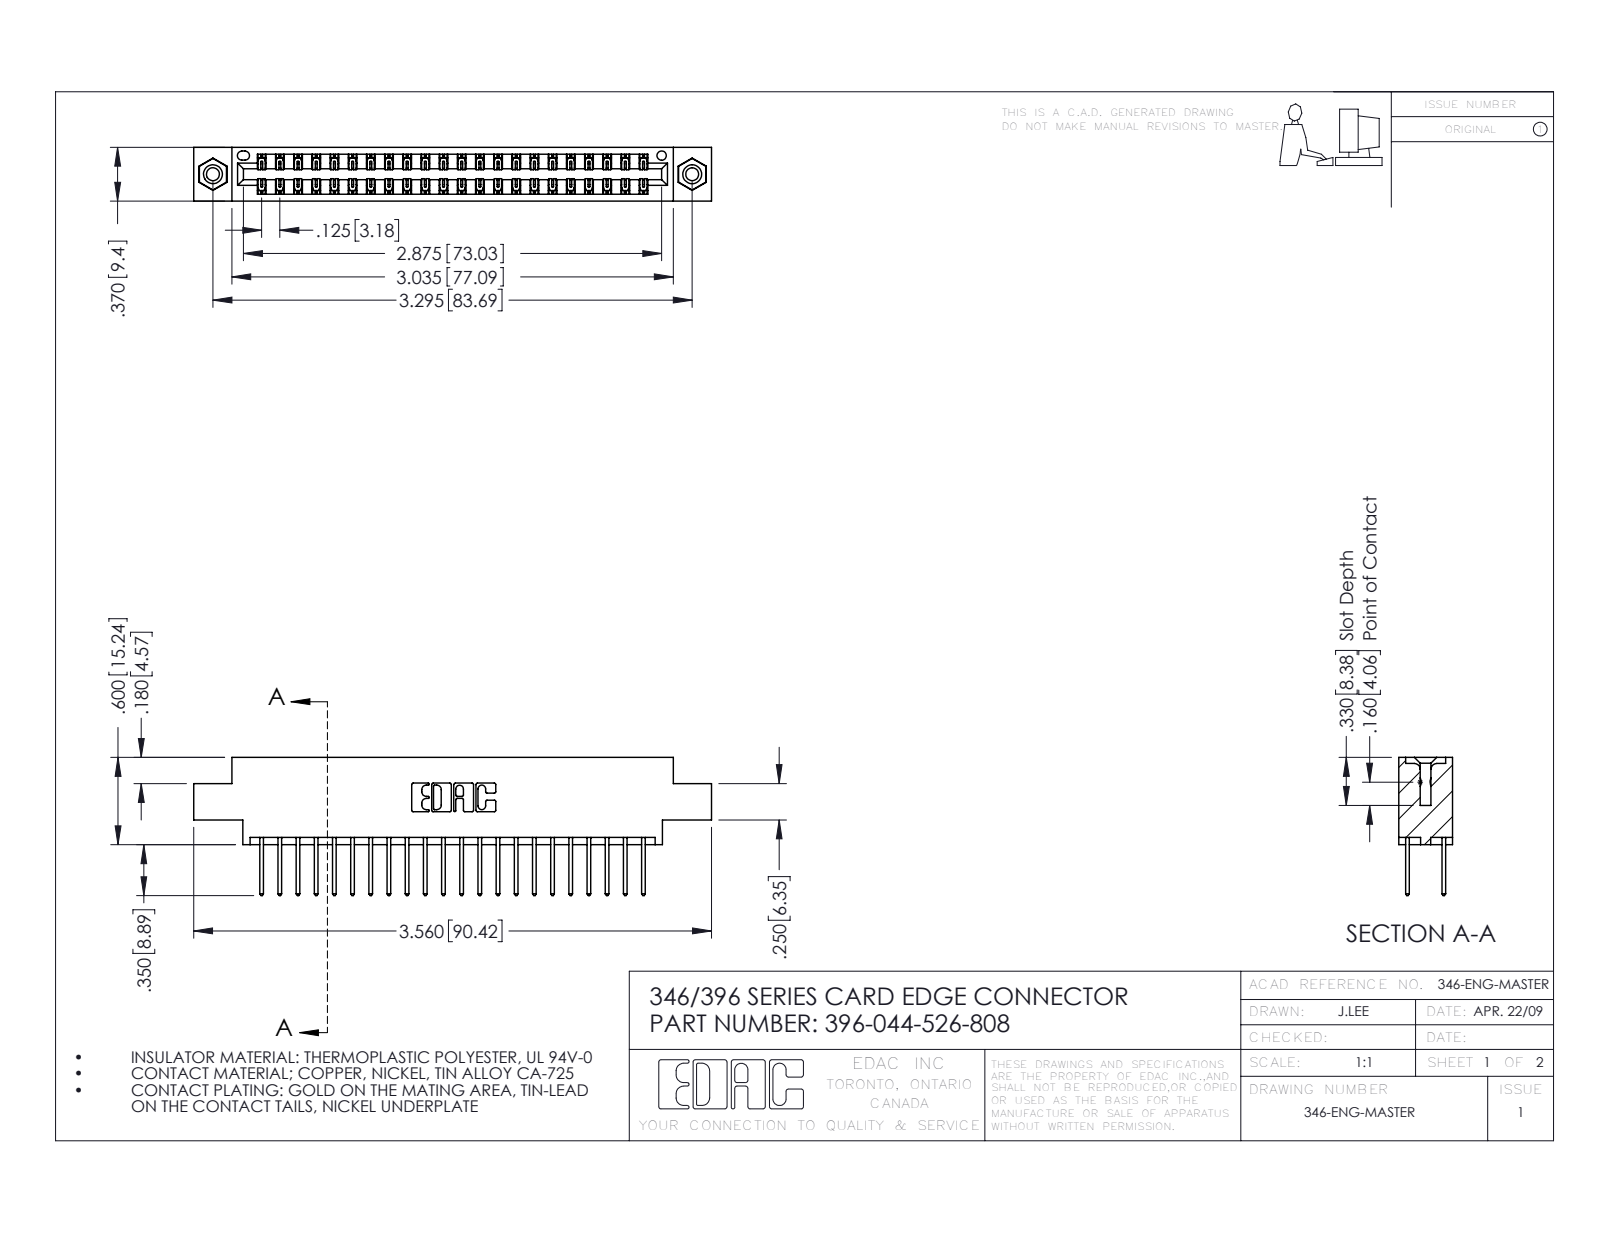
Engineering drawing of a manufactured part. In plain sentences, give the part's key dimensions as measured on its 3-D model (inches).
The part is named "345-292-001_345-293-126; 345-250-001_345-250-003-102; 396-044-526-808; 346 Part_0.170 Offset - 0.156 Dia-TI". Its 3-D file was written by "SolidWorks 2016 (CONFIG_CONTROL_DESIGN)". It is 47 solids with 2474 faces: 1652 planar, 806 cylindrical and 16 other. Overall it measures 3.56 by 0.95 by 0.37 inches. Its volume is 0.523 cubic inches and its surface area 18.59 square inches. Round holes: 2 of diameter 0.089, 2 of diameter 0.125, 2 of diameter 0.156, 1 of diameter 0.064. Round bosses or shafts: 2 of diameter 0.155. Partial cylindrical surfaces (rounded edges, fillets, slot ends): 66 of radius 0.006, 44 of radius 0.01, 22 of radius 0.01, 6 of radius 0.007, 6 of radius 0.031, 3 of radius 0.026, 2 of radius 0.014, 2 of radius 0.022. The main face-to-face distances are 0.048, 0.322, 0.25, 0.37, 0.072, 0.298, 0.025, 0.275, 0.222, 0.148. The hole center spacings are 0.246, 3.087, 3.295.
